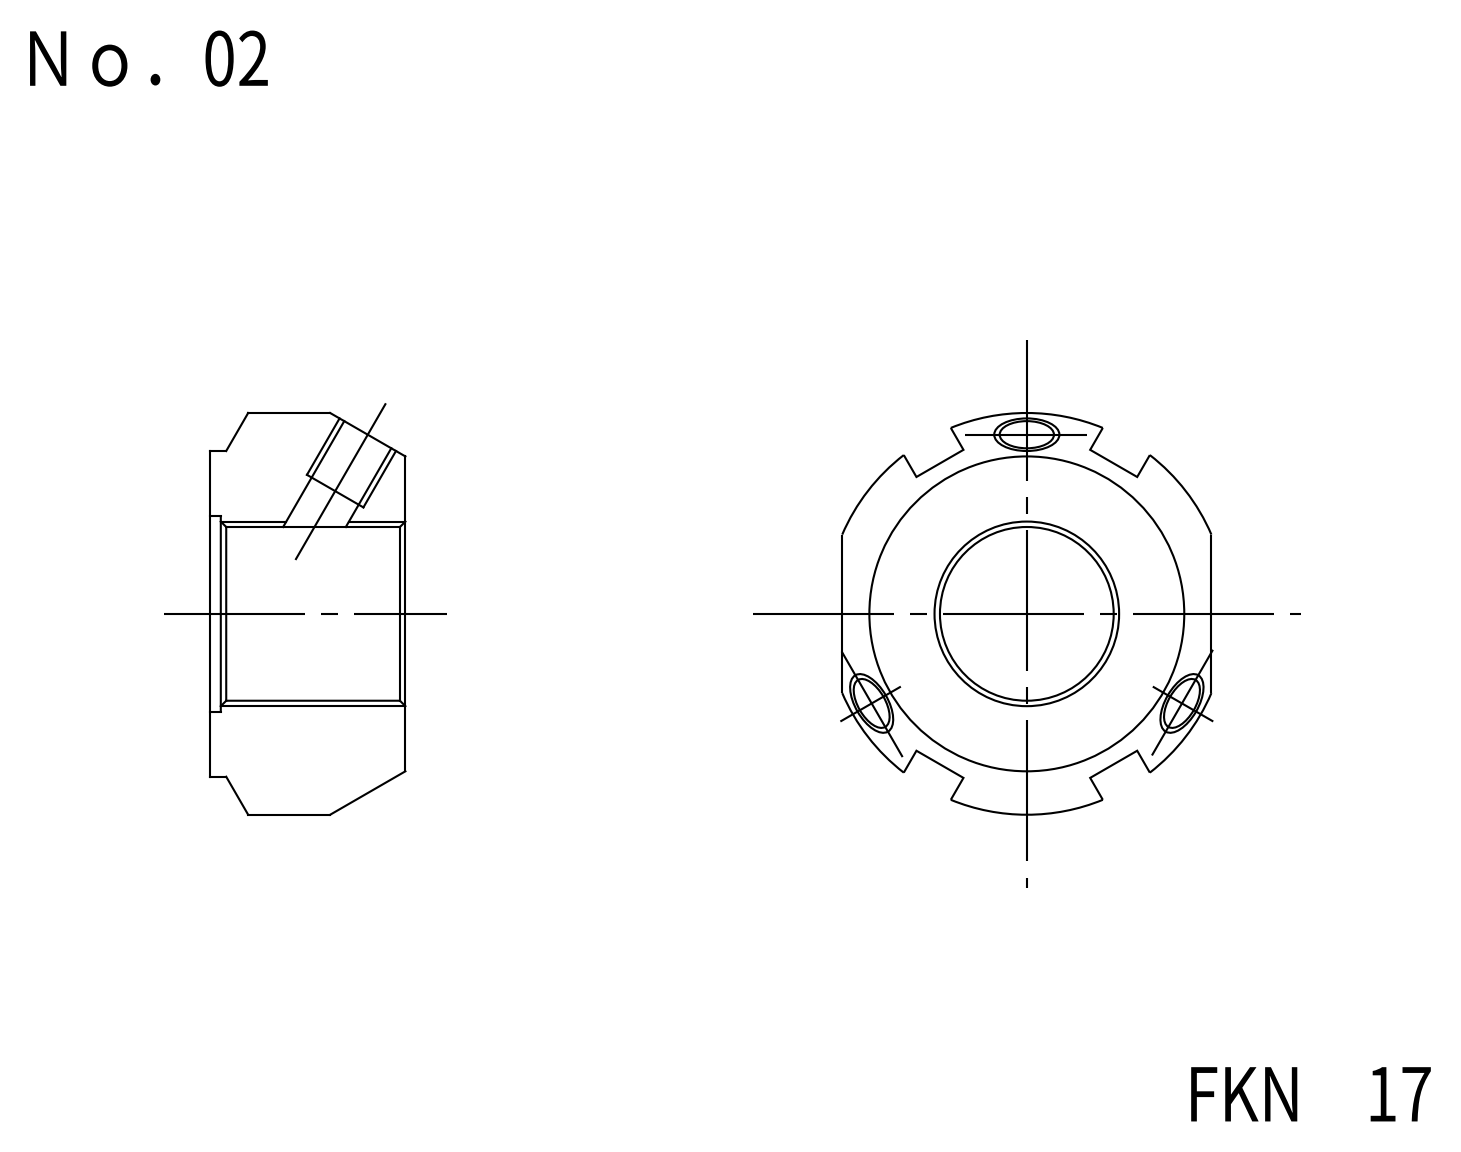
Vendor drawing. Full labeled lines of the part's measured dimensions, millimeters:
Part name (STEP PRODUCT): FKD FKN17
STEP written by: Autodesk Inventor LT (CONFIG_CONTROL_DESIGN)
Units: millimetres
Bodies: 1 solid, 37 faces (20 planar, 15 cylindrical, 2 other)
Overall size (bounding box): 37 × 34 × 18
Volume: 11 503 mm³ · Surface area: 4 568 mm²
Round holes (diameter × count): ⌀6.1 ×3, ⌀4.92 ×2, ⌀4.92 ×1, ⌀17 ×1, ⌀18 ×1
Round bosses / shafts (diameter × count): ⌀30 ×1
Partial cylindrical surfaces — rounded edges, fillets, slot ends (radius × count): R18.5 ×1
Main face-to-face distances: 18, 34, 32, 5, 1.5, 16.5
